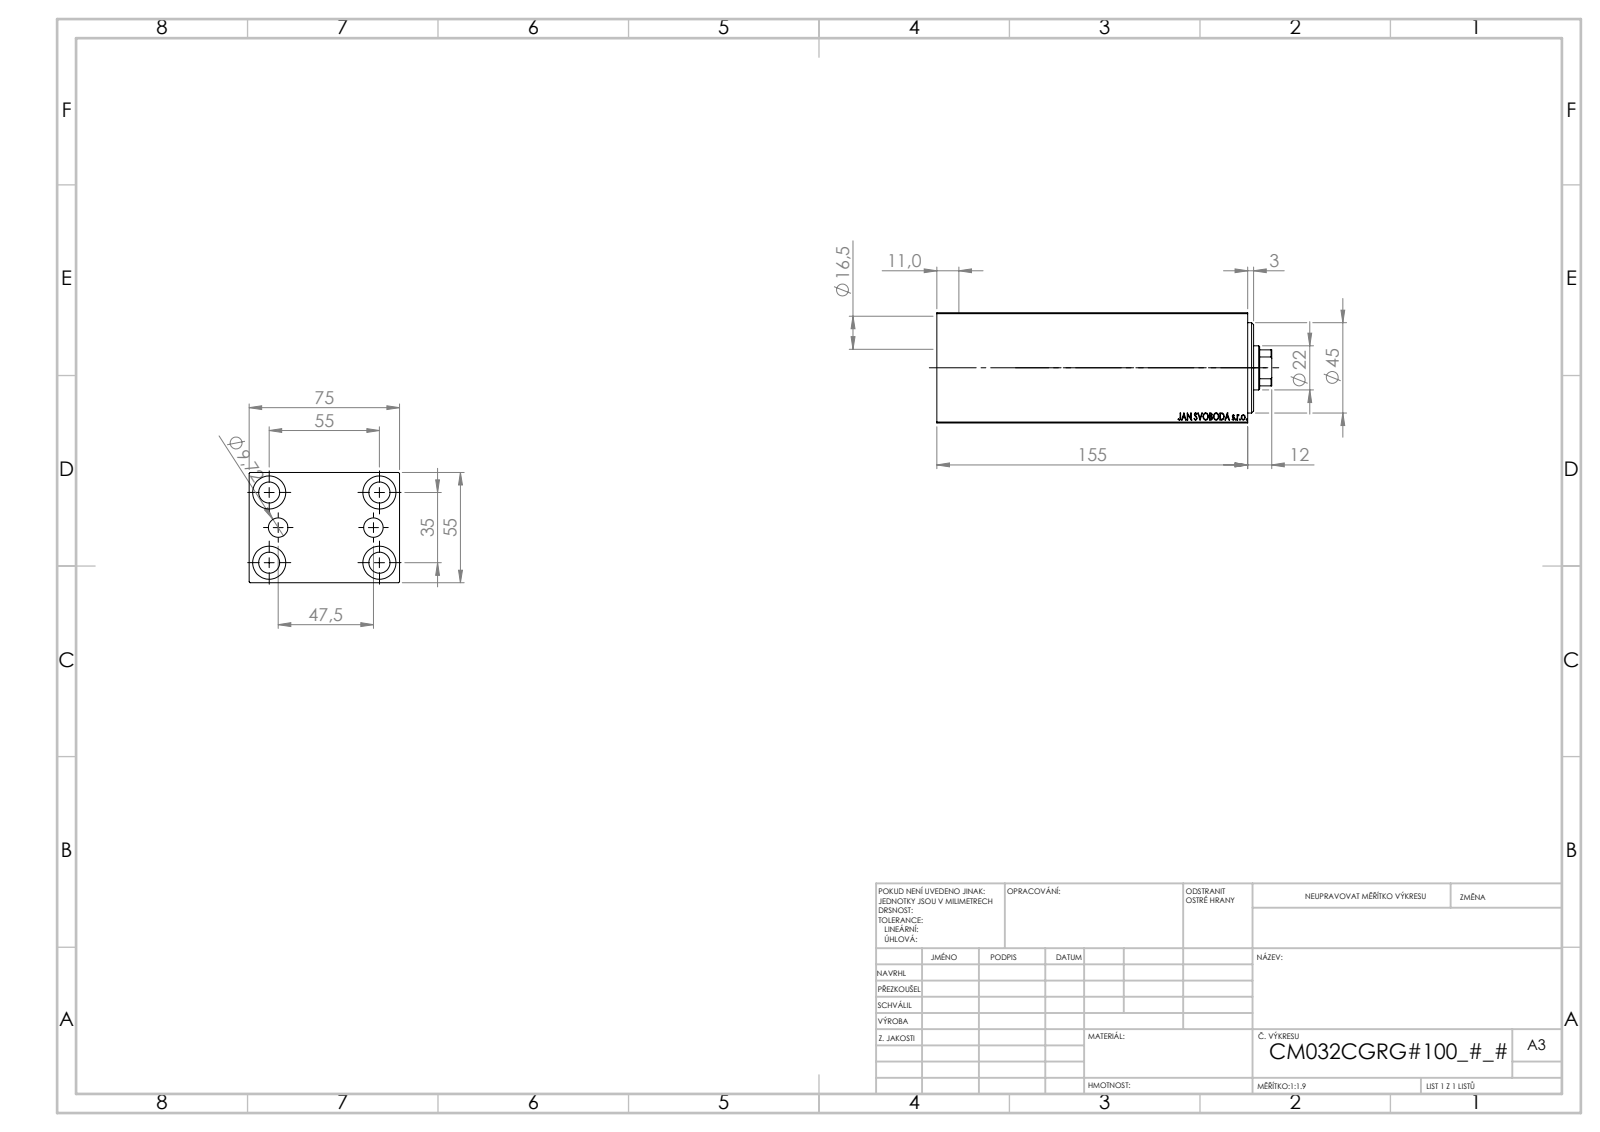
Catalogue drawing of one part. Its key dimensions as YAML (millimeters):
part_name: "V450CM_C_Body; V450CM_VC_B; V450CM_C_VCP"
step_written_by: "SolidWorks 2019 (CONFIG_CONTROL_DESIGN)"
units: millimeters
bodies: {solids: 3, faces: 858, planar: 408, cylindrical: 56, other: 394}
overall_size: [167, 75, 55]
volume: 532794
surface_area: 104009
round_holes:
  - {diameter: 10.5, count: 5}
  - {diameter: 16.5, count: 4}
  - {diameter: 4, count: 2}
  - {diameter: 9.72, count: 2}
  - {diameter: 22, count: 1}
  - {diameter: 25.5, count: 1}
  - {diameter: 32, count: 1}
  - {diameter: 34, count: 1}
  - {diameter: 45, count: 1}
partial_cylinders:
  - {radius: 10.5, count: 1}
face_to_face_distances: [55, 75, 5, 28.75, 126.25, 155, 150, 121.25, 11, 144]
hole_center_spacings: [17.9, 32.6, 54.16, 23.75, 35, 55, 65.19, 47.5]
